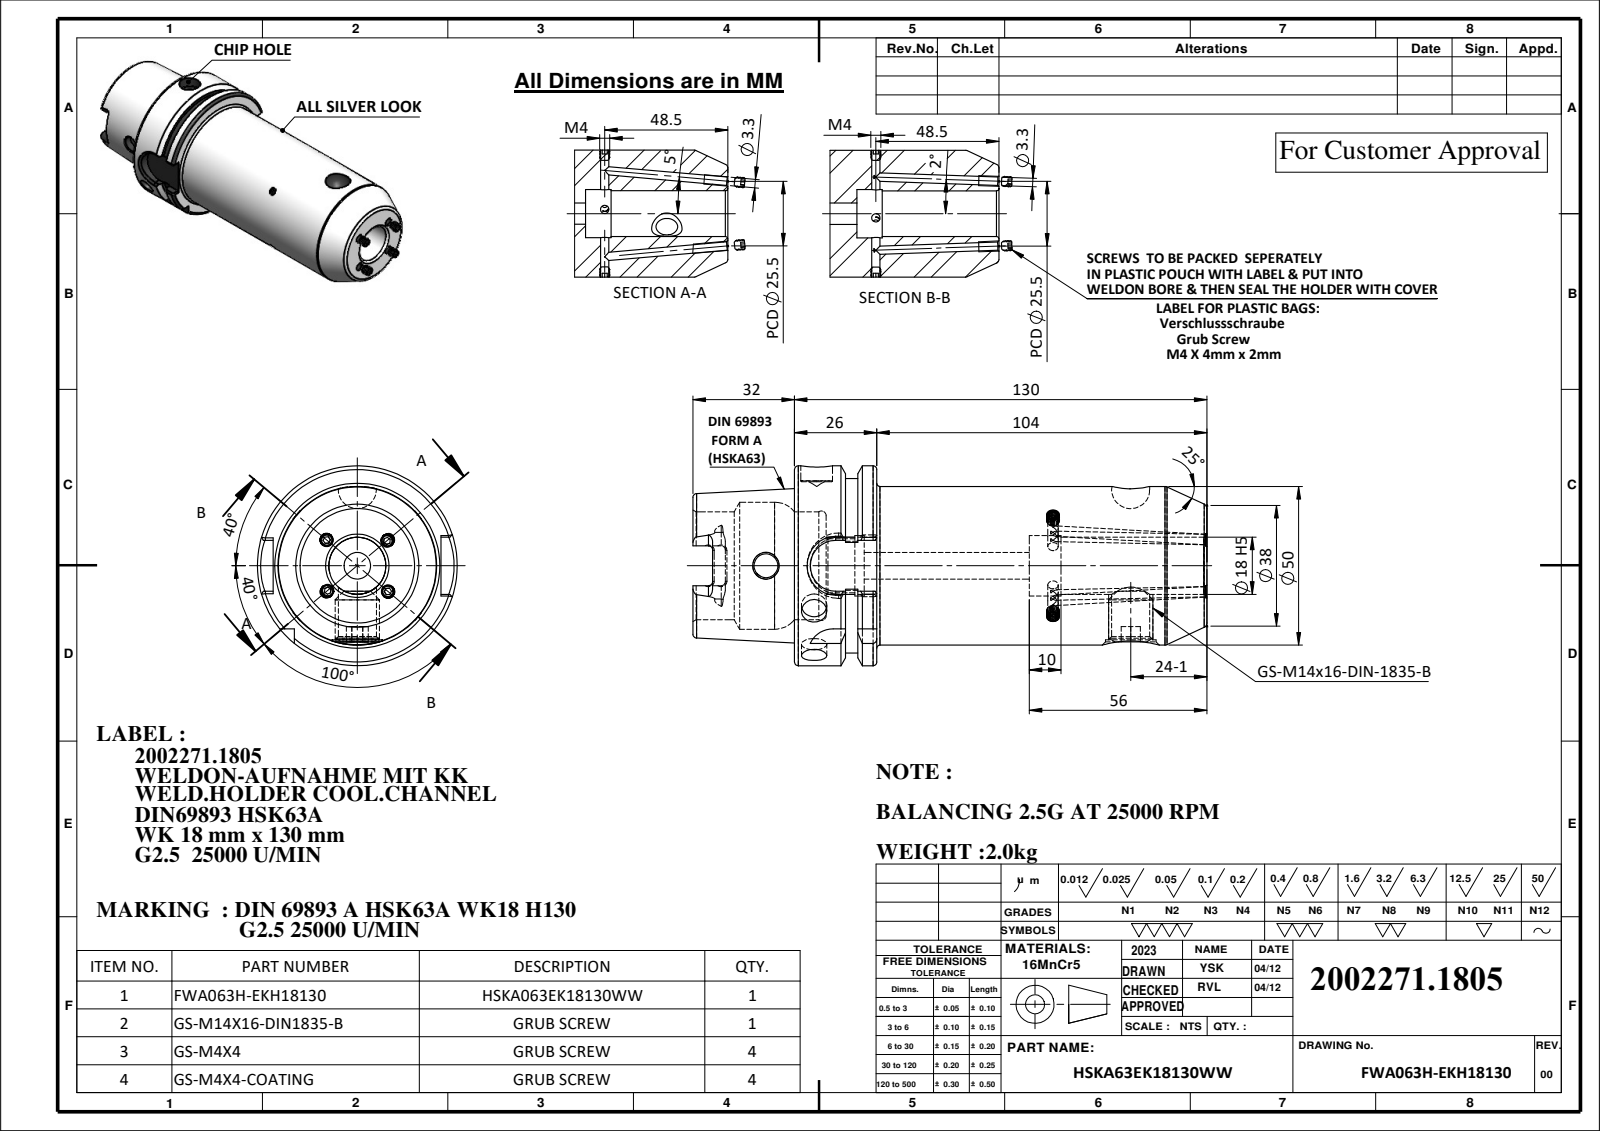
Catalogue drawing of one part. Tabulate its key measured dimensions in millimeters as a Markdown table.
| quantity | value |
| --- | --- |
| part name | FWA063H-EKH18130; HSKA63EK18130WW; GS-M4X4-COATING_DIN 913 - M4 x 4-N; GS-M4X4_DIN 913 - M4 x 4-N (+1 more) |
| STEP written by | SolidWorks 2023 (CONFIG_CONTROL_DESIGN) |
| units | millimeters |
| bodies | 10 solids, 610 faces (133 planar, 165 cylindrical, 312 other) |
| overall size | 168.8 × 63 × 63 |
| volume | 260 057 mm³ |
| surface area | 46 930 mm² |
| round holes (diameter × count) | 3.3 × 8, 8 × 2, 7.5 × 1, 8.4 × 1, 10 × 1, 12 × 1, 16 × 1, 17 × 1, 18 × 1, 19 × 1, 34 × 1, 40 × 1 |
| round bosses / shafts (diameter × count) | 4 × 8, 63 × 1, 55 × 1, 50 × 1, 14 × 1 |
| partial cylindrical surfaces (radius × count) | 1.3 × 6, 2.88 × 4, 8 × 2, 9 × 1 |
| main face-to-face distances | 130, 25.95, 104.05, 10, 15.95, 120, 32, 42, 57.95, 162 |
| hole center spacings | 99 |
